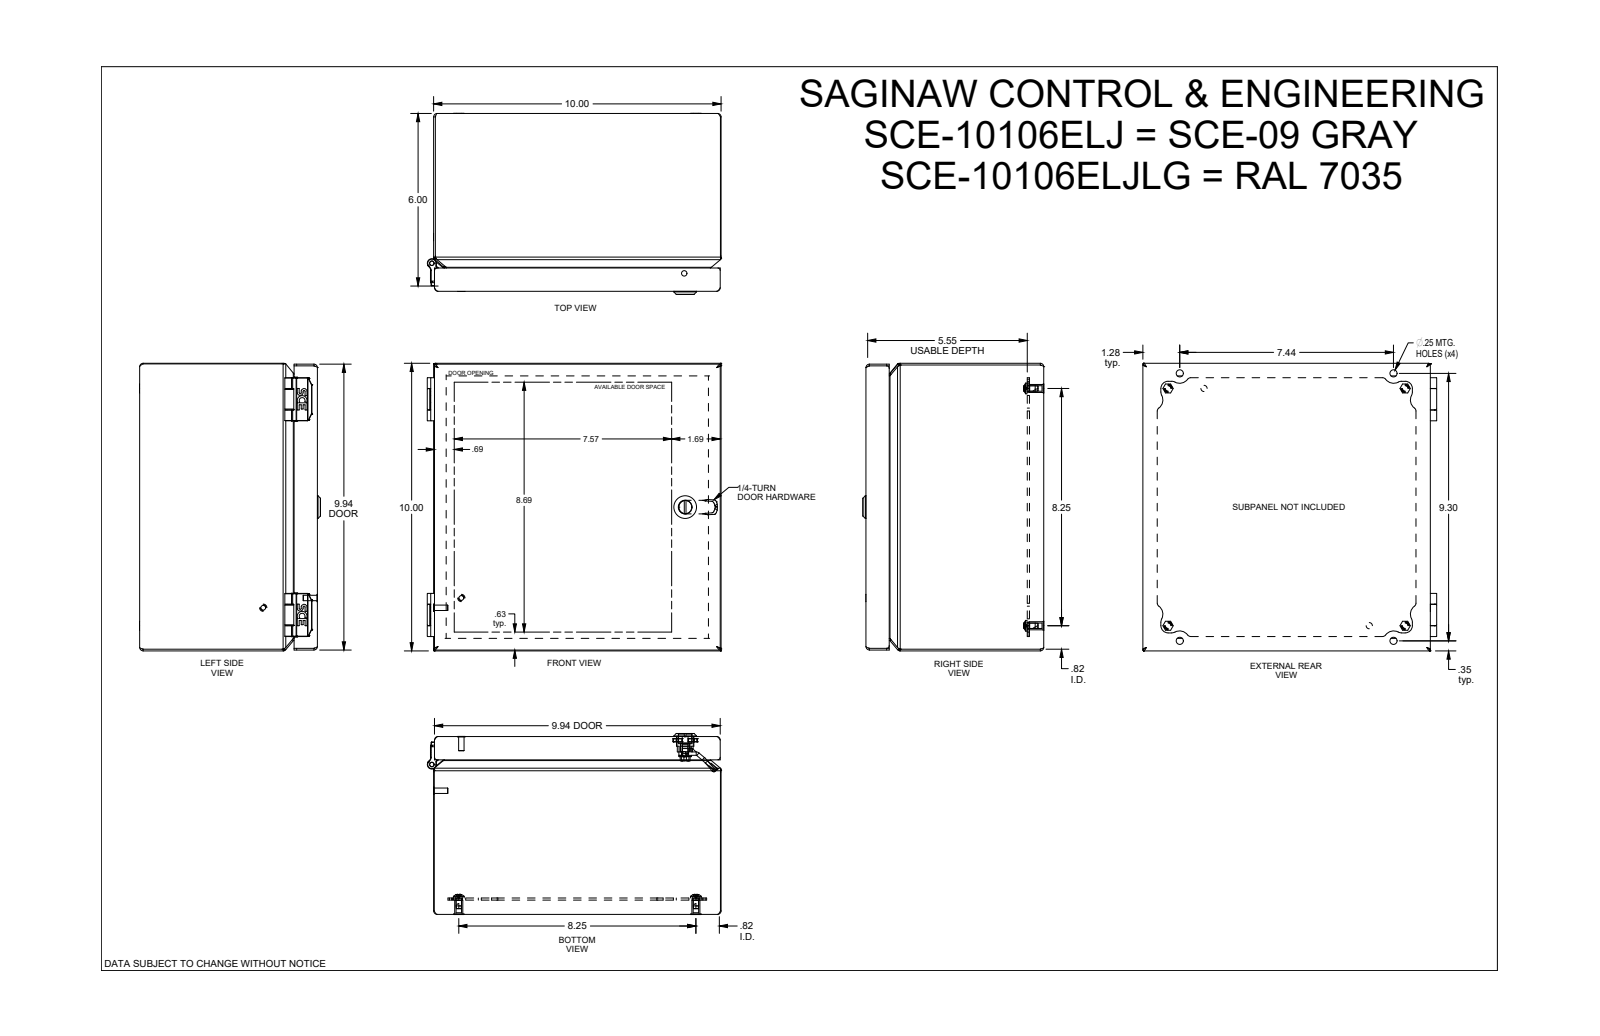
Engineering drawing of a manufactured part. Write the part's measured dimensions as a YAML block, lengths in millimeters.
part_name: "SCE-10106ELJ"
step_written_by: "SolidWorks 2021 (AUTOMOTIVE_DESIGN)"
units: millimeters
bodies: {solids: 34, faces: 1083, planar: 394, cylindrical: 353, other: 336}
overall_size: [259.6, 255.5, 159.9]
volume: 612500
surface_area: 758100
round_holes:
  - {diameter: 6.4, count: 8}
  - {diameter: 4.3, count: 4}
  - {diameter: 4.8, count: 4}
  - {diameter: 7.2, count: 4}
  - {diameter: 0.5, count: 2}
  - {diameter: 2.5, count: 2}
  - {diameter: 5.5, count: 2}
  - {diameter: 6.8, count: 2}
  - {diameter: 4, count: 1}
  - {diameter: 5, count: 1}
  - {diameter: 5.1, count: 1}
  - {diameter: 6.1, count: 1}
round_bosses_or_shafts:
  - {diameter: 4.8, count: 6}
  - {diameter: 12.2, count: 4}
  - {diameter: 9.5, count: 4}
  - {diameter: 7.1, count: 4}
  - {diameter: 4.1, count: 4}
  - {diameter: 6.6, count: 2}
  - {diameter: 6.5, count: 2}
  - {diameter: 6, count: 2}
partial_cylinders:
  - {radius: 0.8, count: 28}
  - {radius: 0.6, count: 24}
  - {radius: 0.3, count: 21}
  - {radius: 1.3, count: 16}
  - {radius: 6.4, count: 13}
  - {radius: 3.2, count: 11}
  - {radius: 0.3, count: 10}
  - {radius: 1.5, count: 10}
face_to_face_distances: [1.5, 254, 1.5, 255.5, 252.5, 157.1, 155.6, 154.1, 155.6, 11.1]
hole_center_spacings: [209.6, 211.1, 190.5, 1.5, 31.8, 105.2, 177.8, 188.9]
